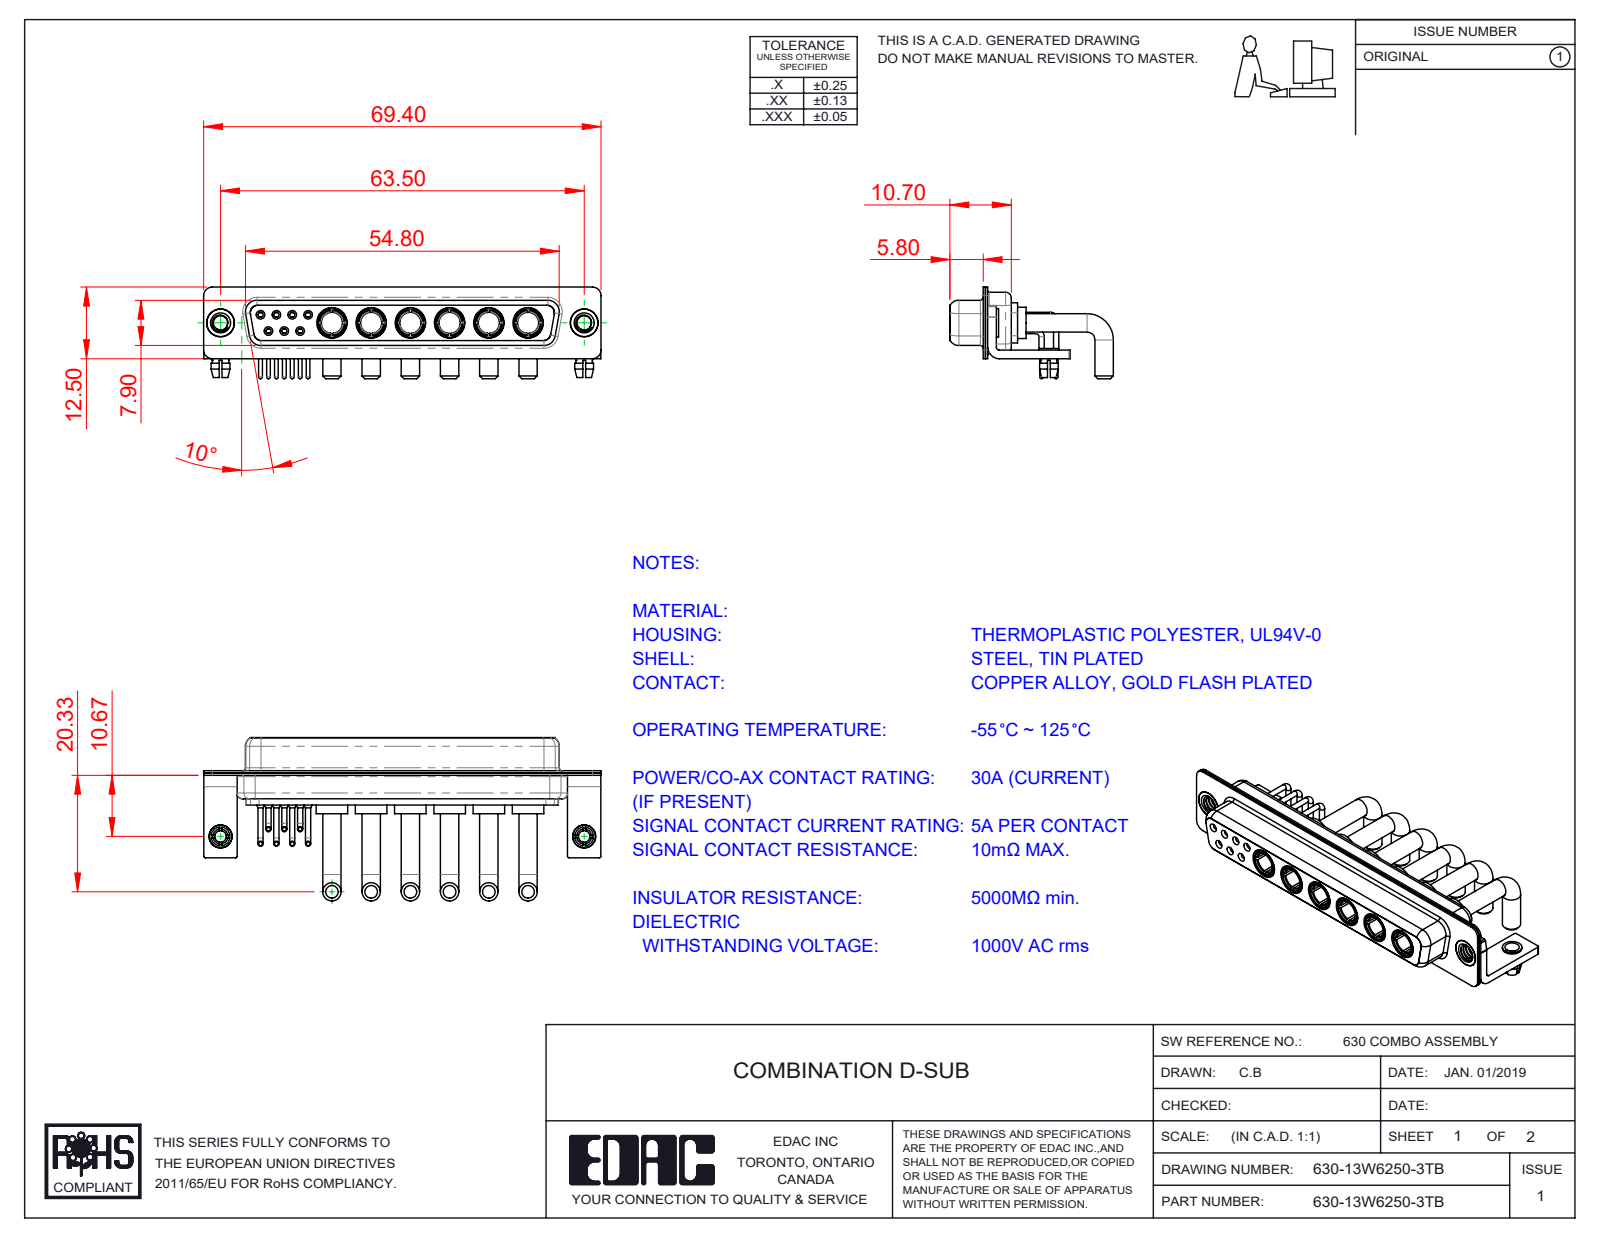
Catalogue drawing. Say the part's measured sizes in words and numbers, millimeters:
The part is named "630Combo Board Lock; 630Combo Shell Rear_37 Contacts; 630Combo Threaded Rivet_B; 630Combo Housing_13W6 (+6 more)". Its 3-D file was written by "SolidWorks 2020 (CONFIG_CONTROL_DESIGN)". It is 28 solids with 1248 faces: 414 planar, 498 cylindrical and 336 other. Overall it measures 69.4 by 28.53 by 16 millimeters. Its volume is 6 486 cubic millimeters and its surface area 13 565 square millimeters. Round holes: 9 of diameter 2, 8 of diameter 4.85, 7 of diameter 0.9, 7 of diameter 1.1, 7 of diameter 1.5, 6 of diameter 3.7, 6 of diameter 5.3, 4 of diameter 1.7, 4 of diameter 2.5, 3 of diameter 1.6, 2 of diameter 3.2, 2 of diameter 4. Round bosses or shafts: 12 of diameter 3.2, 7 of diameter 0.9, 7 of diameter 0.65, 6 of diameter 5.5, 6 of diameter 5.2, 6 of diameter 4.96, 6 of diameter 4.75, 6 of diameter 3.75. Partial cylindrical surfaces (rounded edges, fillets, slot ends): 16 of radius 0.25, 16 of radius 1.5, 13 of radius 2, 8 of radius 1.35, 8 of radius 1.6, 6 of radius 2.1, 5 of radius 0.5, 4 of radius 0.6. The main face-to-face distances are 0.4, 0.45, 1.4, 8.45, 1.8, 8.9, 6.2, 7.05, 7.5, 0.8. The hole center spacings are 3.16, 2.77, 6.85, 13.7, 5.54, 20.55, 5.03, 5.04.
